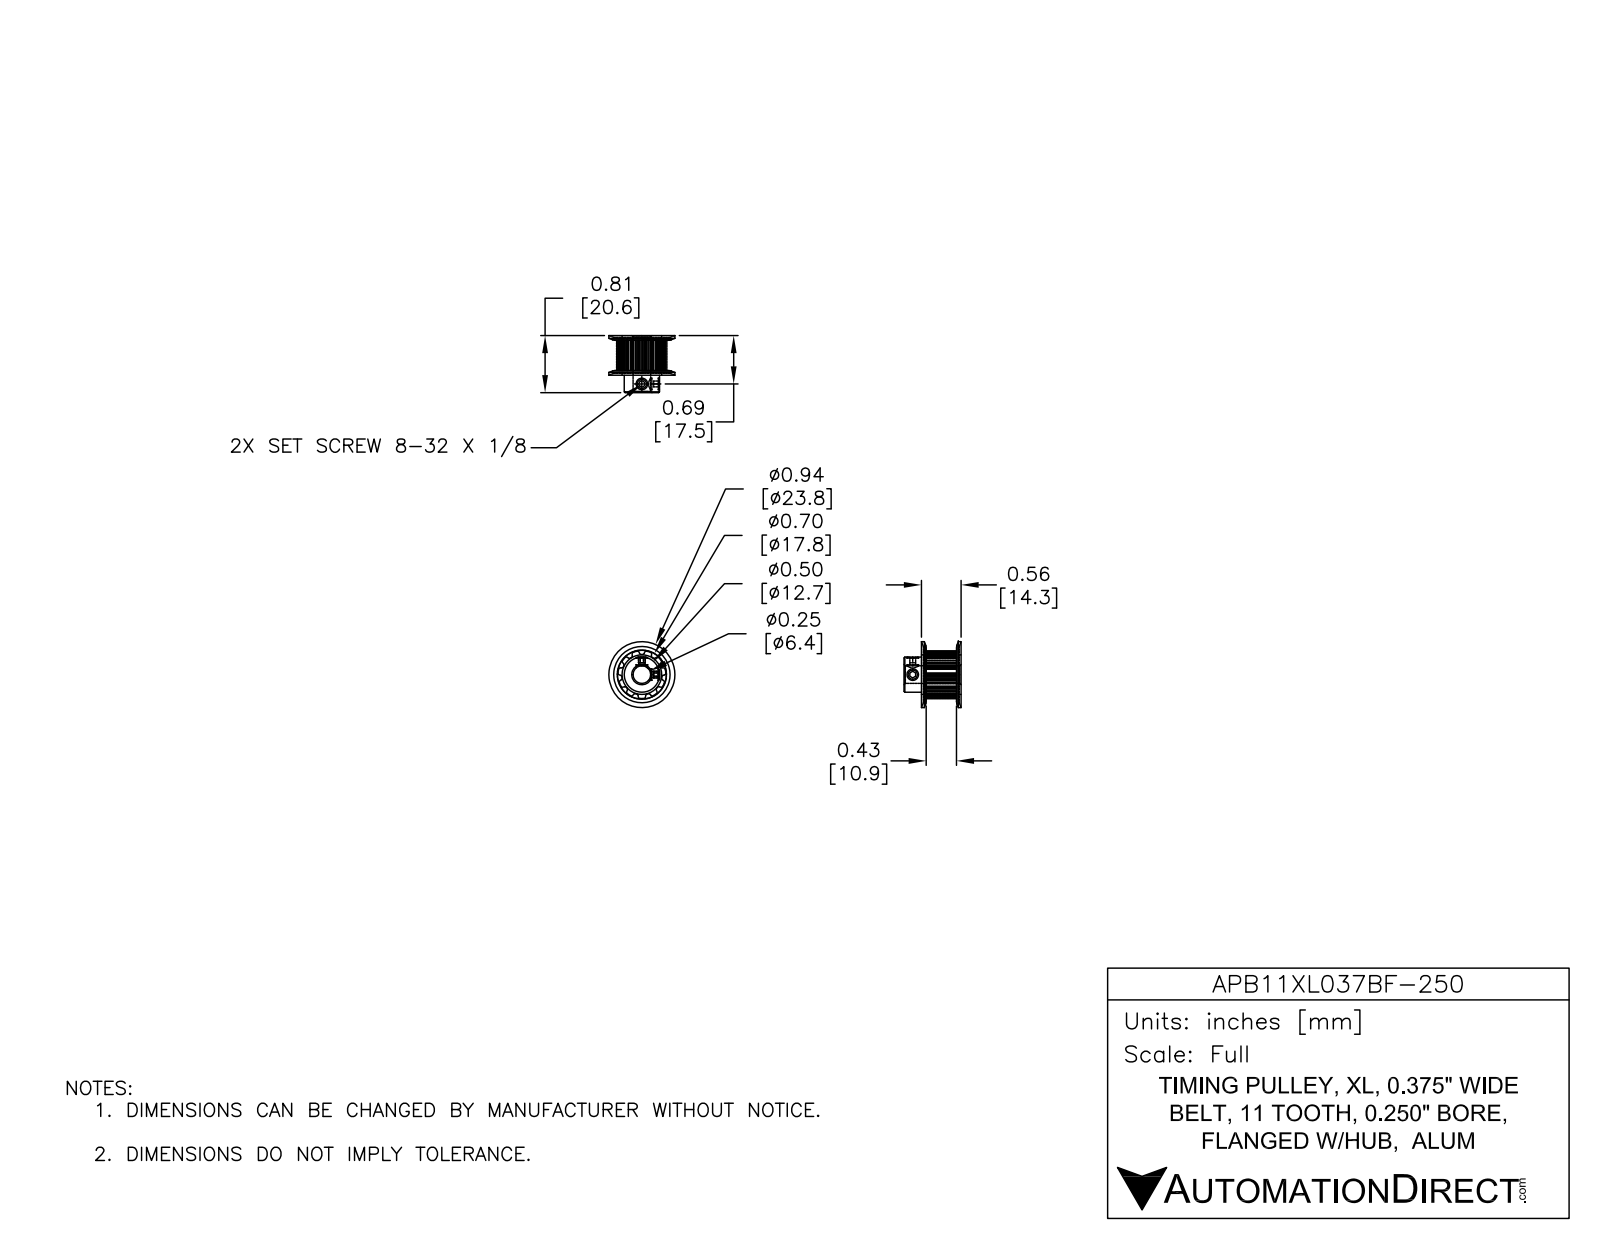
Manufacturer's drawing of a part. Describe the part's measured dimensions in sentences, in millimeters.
The part is named "APB11XL037BF-250". Its 3-D file was written by "SolidWorks 2014 (AUTOMOTIVE_DESIGN)". It is 1 solid with 133 faces: 39 planar, 72 cylindrical and 22 other. Overall it measures 23.8 by 23.8 by 20.7 millimeters. Its volume is 3 310 cubic millimeters and its surface area 2 939 square millimeters. Round holes: 2 of diameter 2.2, 1 of diameter 6.4. Round bosses or shafts: 1 of diameter 12.7. Partial cylindrical surfaces (rounded edges, fillets, slot ends): 44 of radius 0.4, 1 of radius 7.2. The main face-to-face distances are 12.6, 0.8, 13.4, 20.7, 19.8, 7.2, 1.7, 0.8, 11.8, 19.
